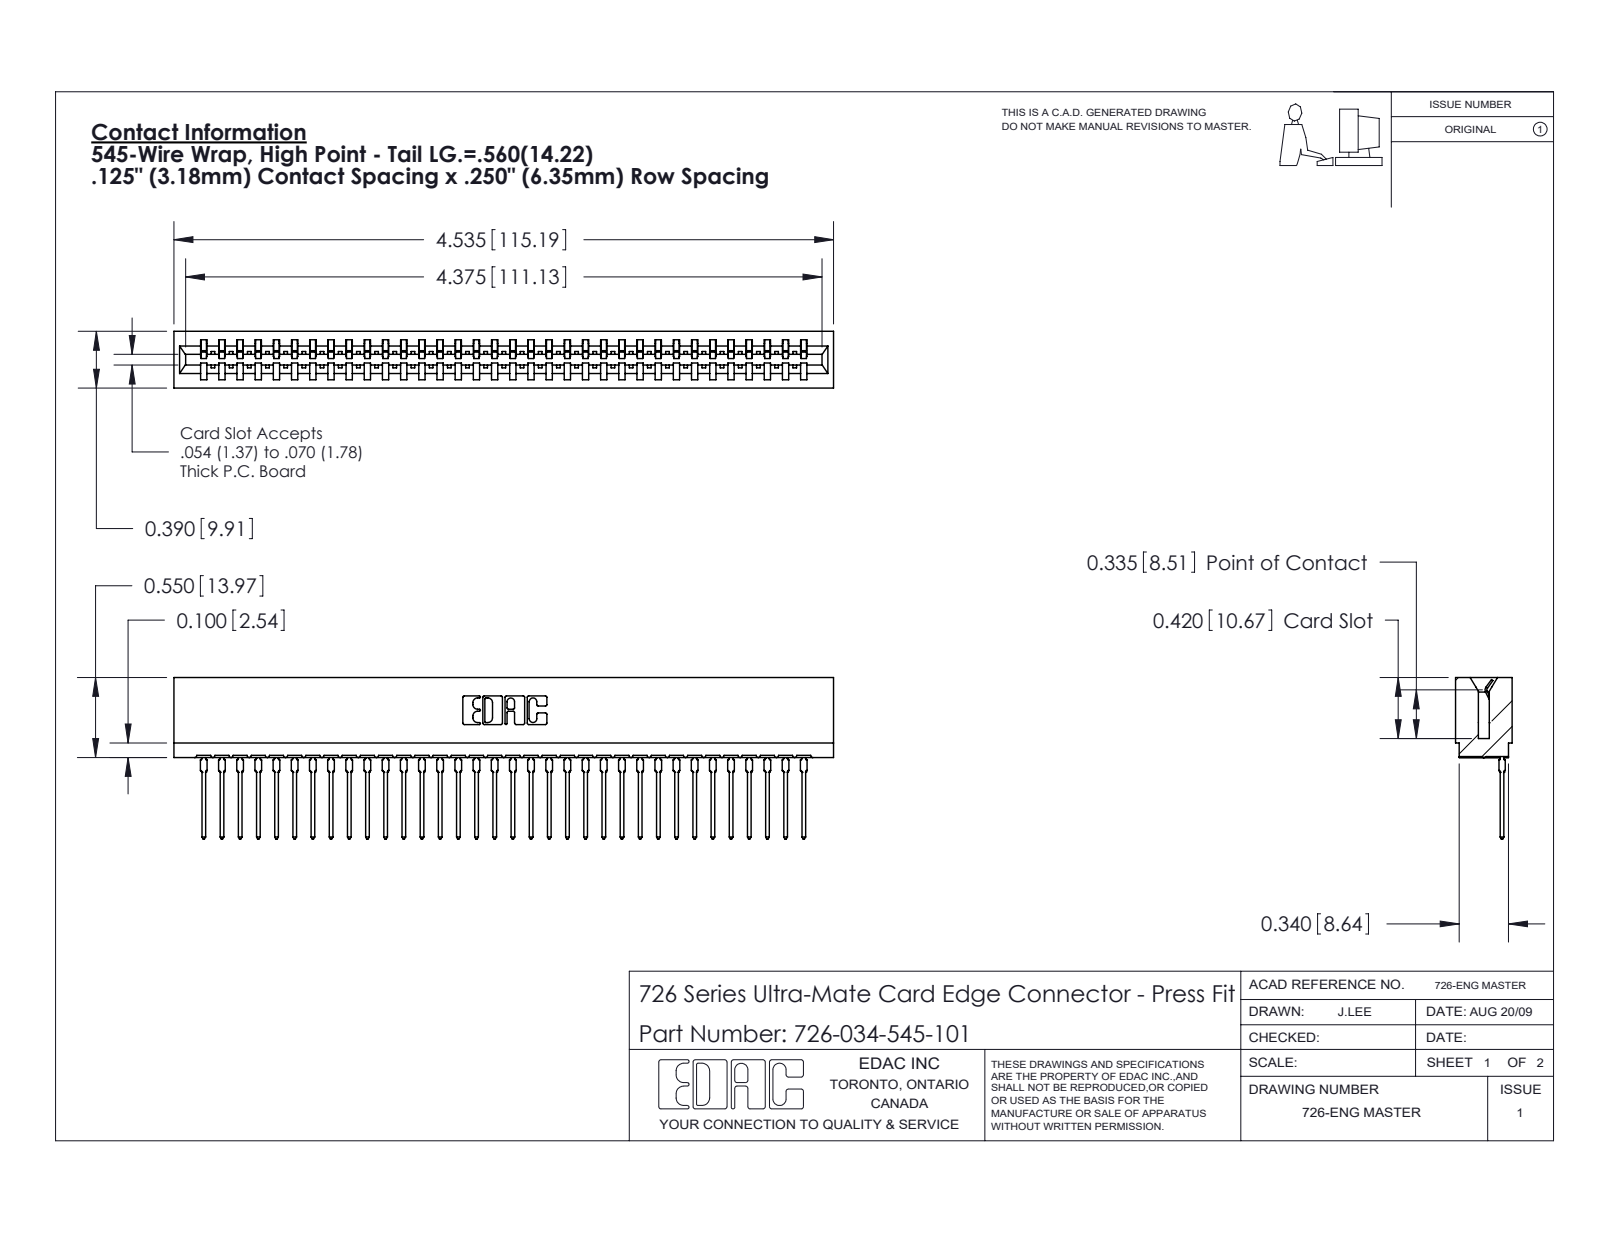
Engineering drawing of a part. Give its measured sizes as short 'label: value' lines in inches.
name: 746-292-001_545; 726 Part_.515 Slot Depth - 01; 726-034-545-101
written by: SolidWorks 2020 (CONFIG_CONTROL_DESIGN)
unit: in
bodies: 35 solids, 3769 faces (2197 planar, 688 cylindrical, 884 other)
size: 4.535 × 1.109 × 0.39
volume: 0.636 in³; area: 25.22 in²
rounds: 68× R0.021, 35× R0.015, 22× R0.01, 6× R0.007, 6× R0.031, 4× R0.005, 4× R0.011, 3× R0.026
face distances: 0.057, 0.333, 0.39, 0.025, 0.307, 0.25, 0.083, 0.275, 0.365, 0.032
